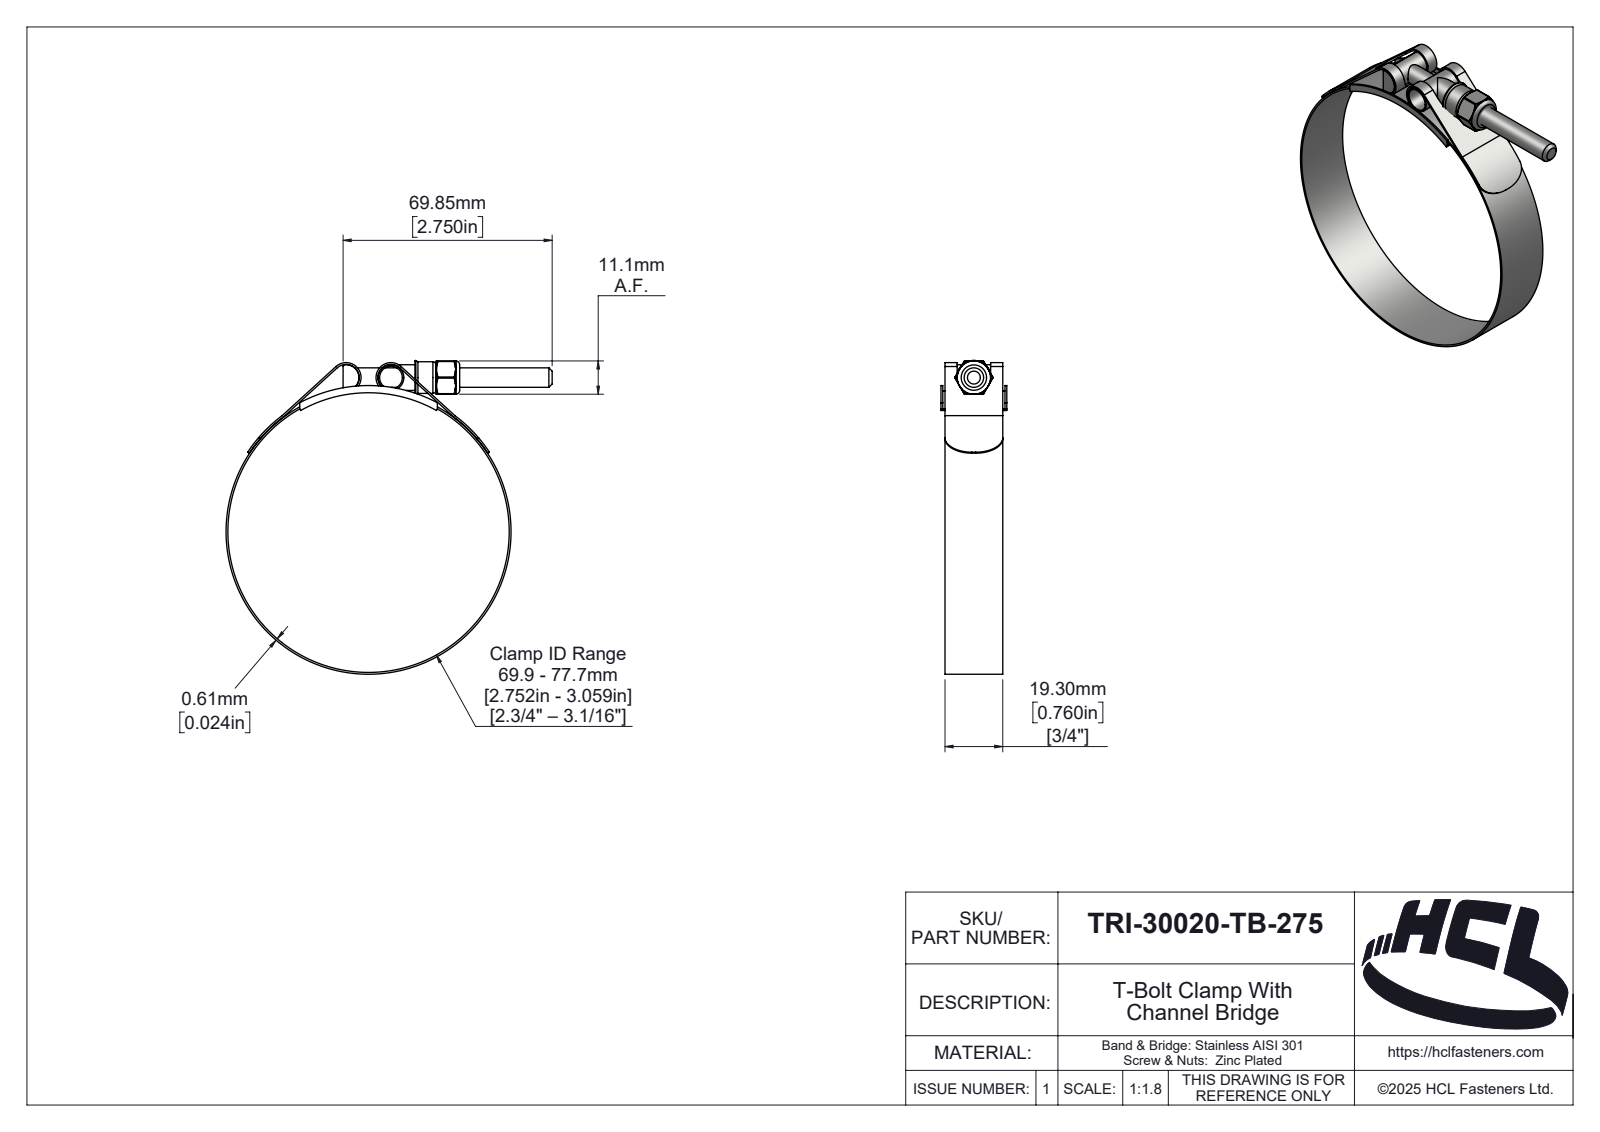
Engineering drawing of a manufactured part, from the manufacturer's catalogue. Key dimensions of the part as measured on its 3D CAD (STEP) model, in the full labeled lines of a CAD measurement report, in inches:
Part name (STEP PRODUCT): TRI-30020-TB-275
STEP written by: SolidWorks 2025 (AUTOMOTIVE_DESIGN)
Units: inches
Bodies: 6 solids, 330 faces (44 planar, 122 cylindrical, 164 other)
Overall size (bounding box): 4.29 × 4.126 × 0.866
Volume: 0.566 in³ · Surface area: 33.62 in²
Round holes (diameter × count): ⌀0.213 ×1, ⌀0.25 ×1, ⌀0.256 ×1, ⌀0.298 ×1, ⌀3.701 ×1
Round bosses / shafts (diameter × count): ⌀0.338 ×2, ⌀3.749 ×1, ⌀0.417 ×1
Partial cylindrical surfaces — rounded edges, fillets, slot ends (radius × count): R0.015 ×6, R0.02 ×2, R0.173 ×2, R0.197 ×2, R0.023 ×1, R0.095 ×1, R0.119 ×1, R0.126 ×1
Main face-to-face distances: 0.024, 0.76, 0.053, 0.813, 0.029, 0.842, 0.789, 0.866, 0.437, 0.818
Hole centre spacings: 2.047
